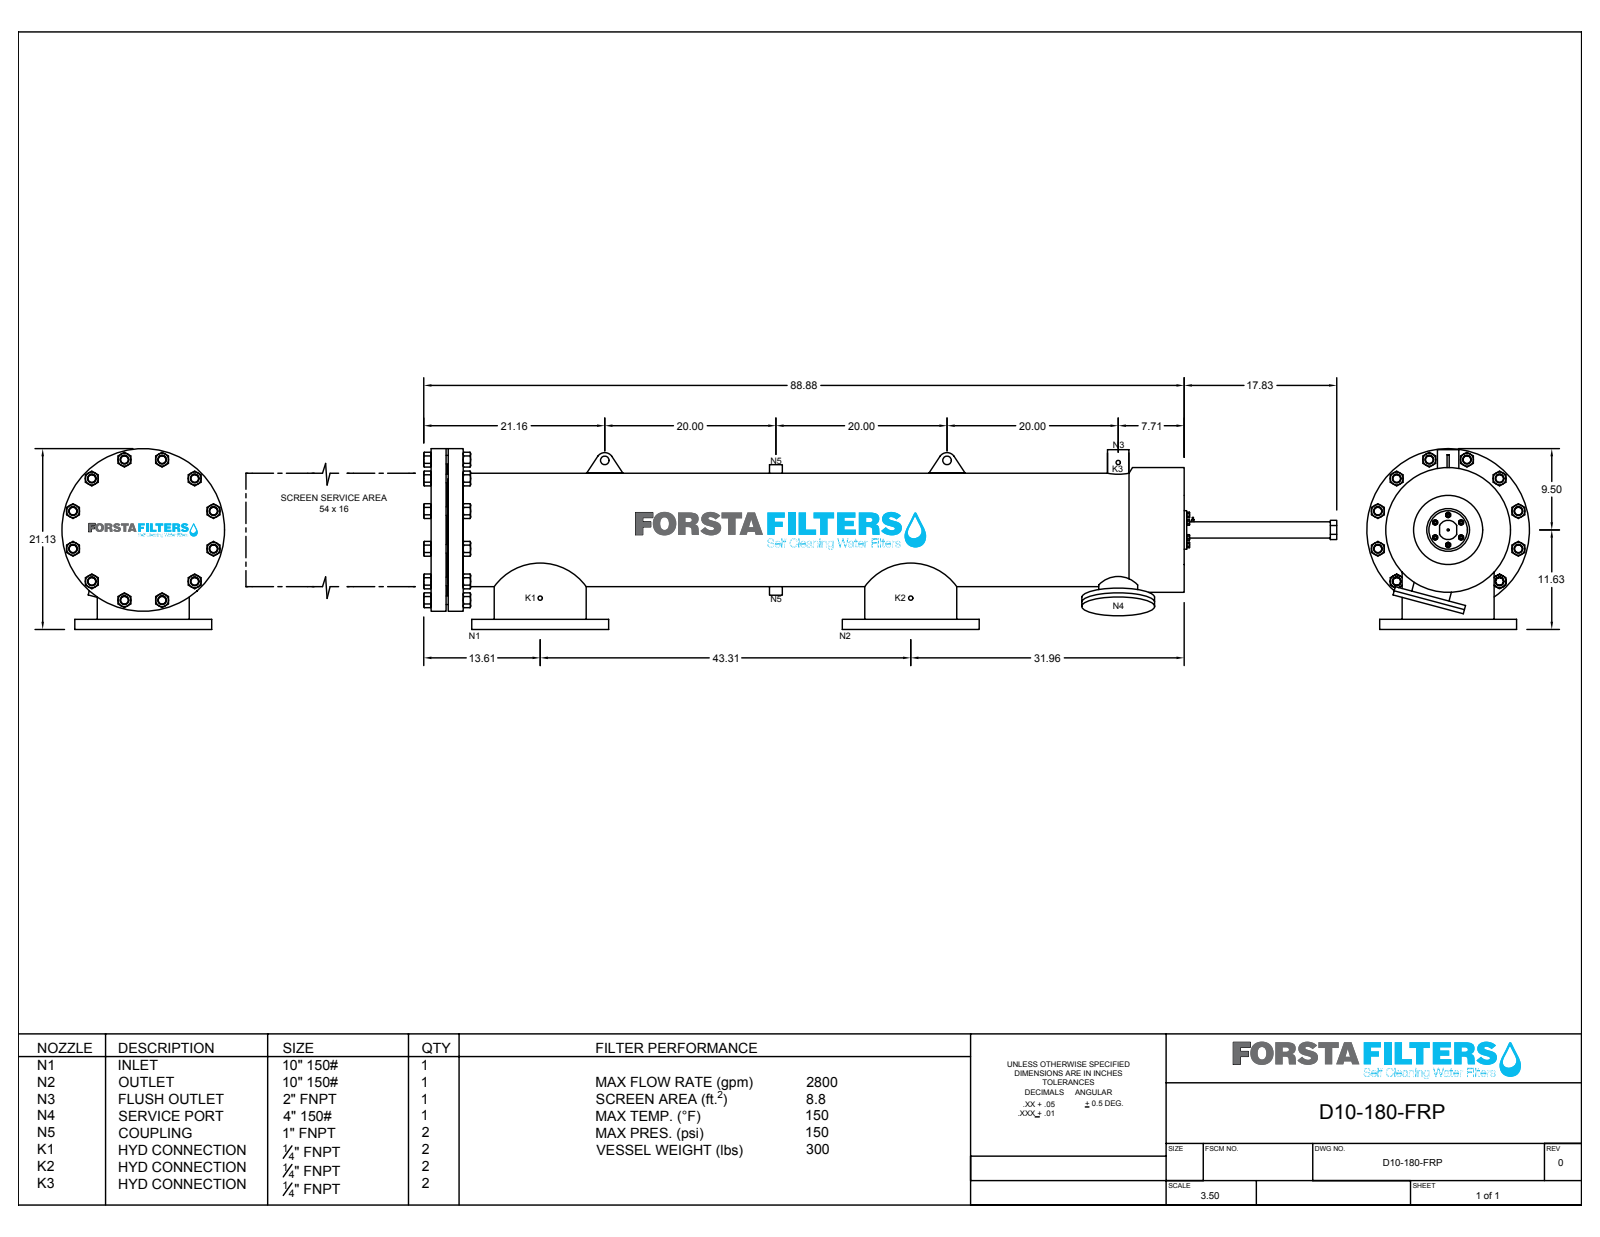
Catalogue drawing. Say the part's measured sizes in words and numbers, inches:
The part is named "D10-FRP-180". Its 3-D file was written by "SolidWorks 2018 (CONFIG_CONTROL_DESIGN)". It is 19 solids with 667 faces: 299 planar, 350 cylindrical and 18 other. Overall it measures 105.19 by 21.13 by 19 inches. Its volume is 1 991 cubic inches and its surface area 11 066 square inches. Round holes: 31 of diameter 1, 16 of diameter 0.75, 5 of diameter 0.375, 4 of diameter 0.25, 2 of diameter 4.5, 2 of diameter 10, 1 of diameter 0.375, 1 of diameter 1.506, 1 of diameter 2, 1 of diameter 12.86, 1 of diameter 14.187. Round bosses or shafts: 5 of diameter 0.375, 3 of diameter 0.644, 2 of diameter 16, 2 of diameter 10.394, 2 of diameter 9, 2 of diameter 4.894, 1 of diameter 19, 1 of diameter 14.581. Partial cylindrical surfaces (rounded edges, fillets, slot ends): 2 of radius 1, 1 of radius 1.125. The main face-to-face distances are 2, 1.12, 0.5, 88.707, 86.707, 88.51, 86.51, 0.197, 3.75, 1.75. The hole center spacings are 2.87, 3.75, 5.303, 6.929, 8.5, 10.076, 5.454, 9.111.
